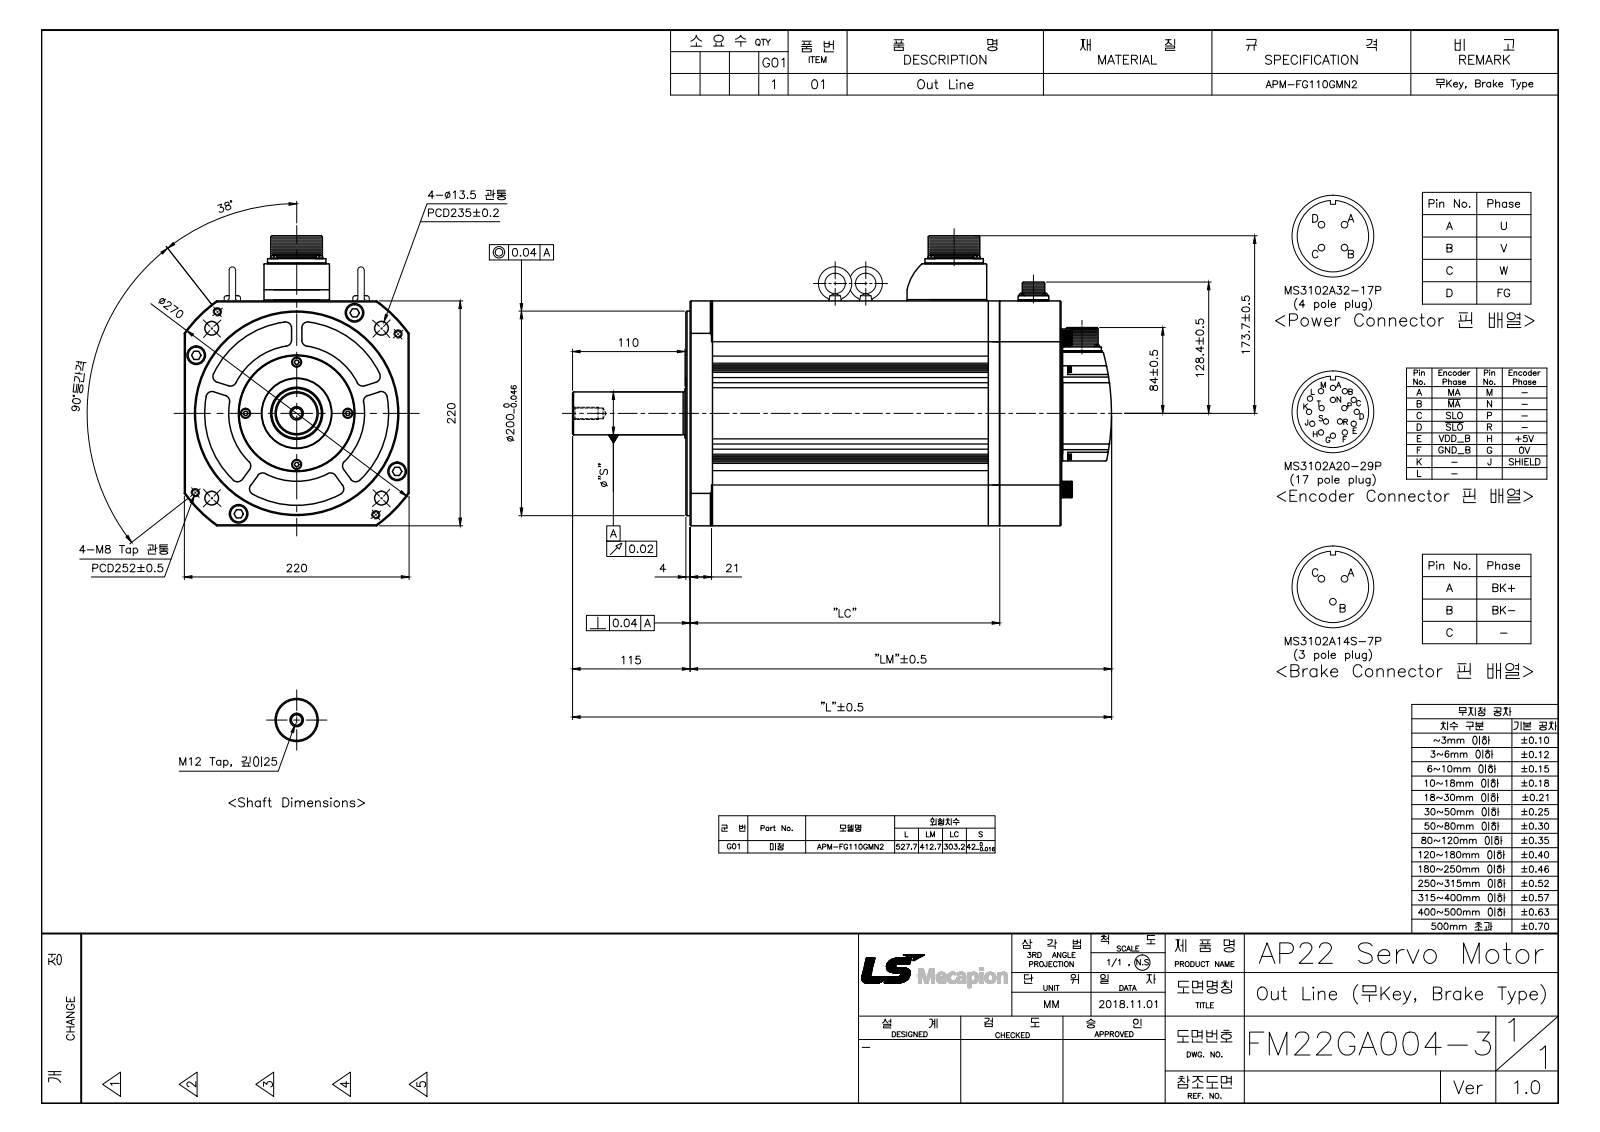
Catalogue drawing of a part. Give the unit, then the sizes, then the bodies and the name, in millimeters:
Units: millimetres
Overall size (bounding box): 527.7 × 283.7 × 220
Round holes (diameter × count): ⌀2.5 ×12, ⌀3 ×12, ⌀3.05 ×10, ⌀8 ×8, ⌀11.2 ×7, ⌀17.5 ×7, ⌀18 ×5, ⌀3.3 ×4, ⌀3.5 ×4, ⌀3.6 ×4, ⌀3.7 ×4, ⌀4 ×4
Round bosses / shafts (diameter × count): ⌀1.6 ×20, ⌀5.4 ×8, ⌀16 ×7, ⌀8.5 ×4, ⌀7 ×4, ⌀6 ×4, ⌀5.5 ×4, ⌀10 ×3
Partial cylindrical surfaces — rounded edges, fillets, slot ends (radius × count): R1 ×122, R6 ×24, R2 ×17, R5 ×16, R4 ×14, R4.5 ×12, R0.5 ×8, R2.5 ×4
Main face-to-face distances: 11.2, 281.2, 270, 40, 220, 180, 140, 21, 14, 60
Hole centre spacings: 89.44, 156.9, 16.26, 17.11, 20.79, 23, 27.23, 29.4
Volume: 15 880 000 mm³ · Surface area: 991 537 mm²
Bodies: 73 solids, 2557 faces (890 planar, 1004 cylindrical, 663 other)
Part name (STEP PRODUCT): FM22GA004-3_Out Line(APM-FG110G_N2)
STEP written by: SolidWorks 2011 (AUTOMOTIVE_DESIGN)
